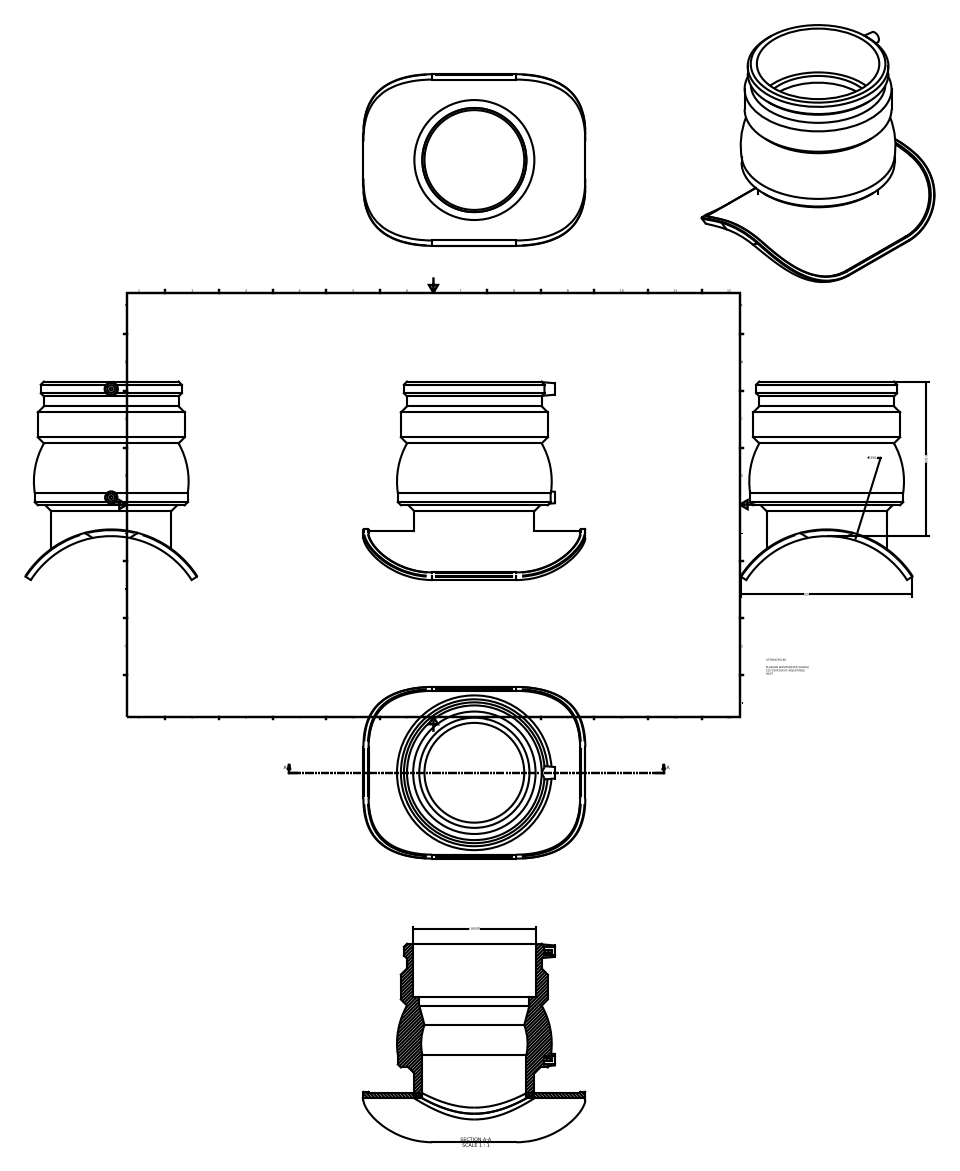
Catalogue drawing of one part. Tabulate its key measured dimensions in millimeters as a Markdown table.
| quantity | value |
| --- | --- |
| part name | 475804250160 |
| STEP written by | Autodesk Inventor 2015 (AUTOMOTIVE_DESIGN) |
| units | millimeters |
| bodies | 2 solids, 69 faces (17 planar, 29 cylindrical, 23 other) |
| overall size | 290 × 259.39 × 224.31 |
| volume | 2 491 000 mm³ |
| surface area | 368 259 mm² |
| round holes (diameter × count) | 10 × 2, 136 × 1, 144 × 1, 160 × 1 |
| round bosses / shafts (diameter × count) | 4 × 2, 200 × 1, 192 × 1, 184 × 1, 176 × 1, 156.8 × 1 |
| partial cylindrical surfaces (radius × count) | 0.9 × 4, 83.25 × 4, 90 × 4, 125 × 1, 131.75 × 1, 133.75 × 1 |
| main face-to-face distances | 161.6, 91.6, 70, 290, 6.75, 250, 40, 283.25, 236, 14 |
| hole center spacings | 141.82 |
